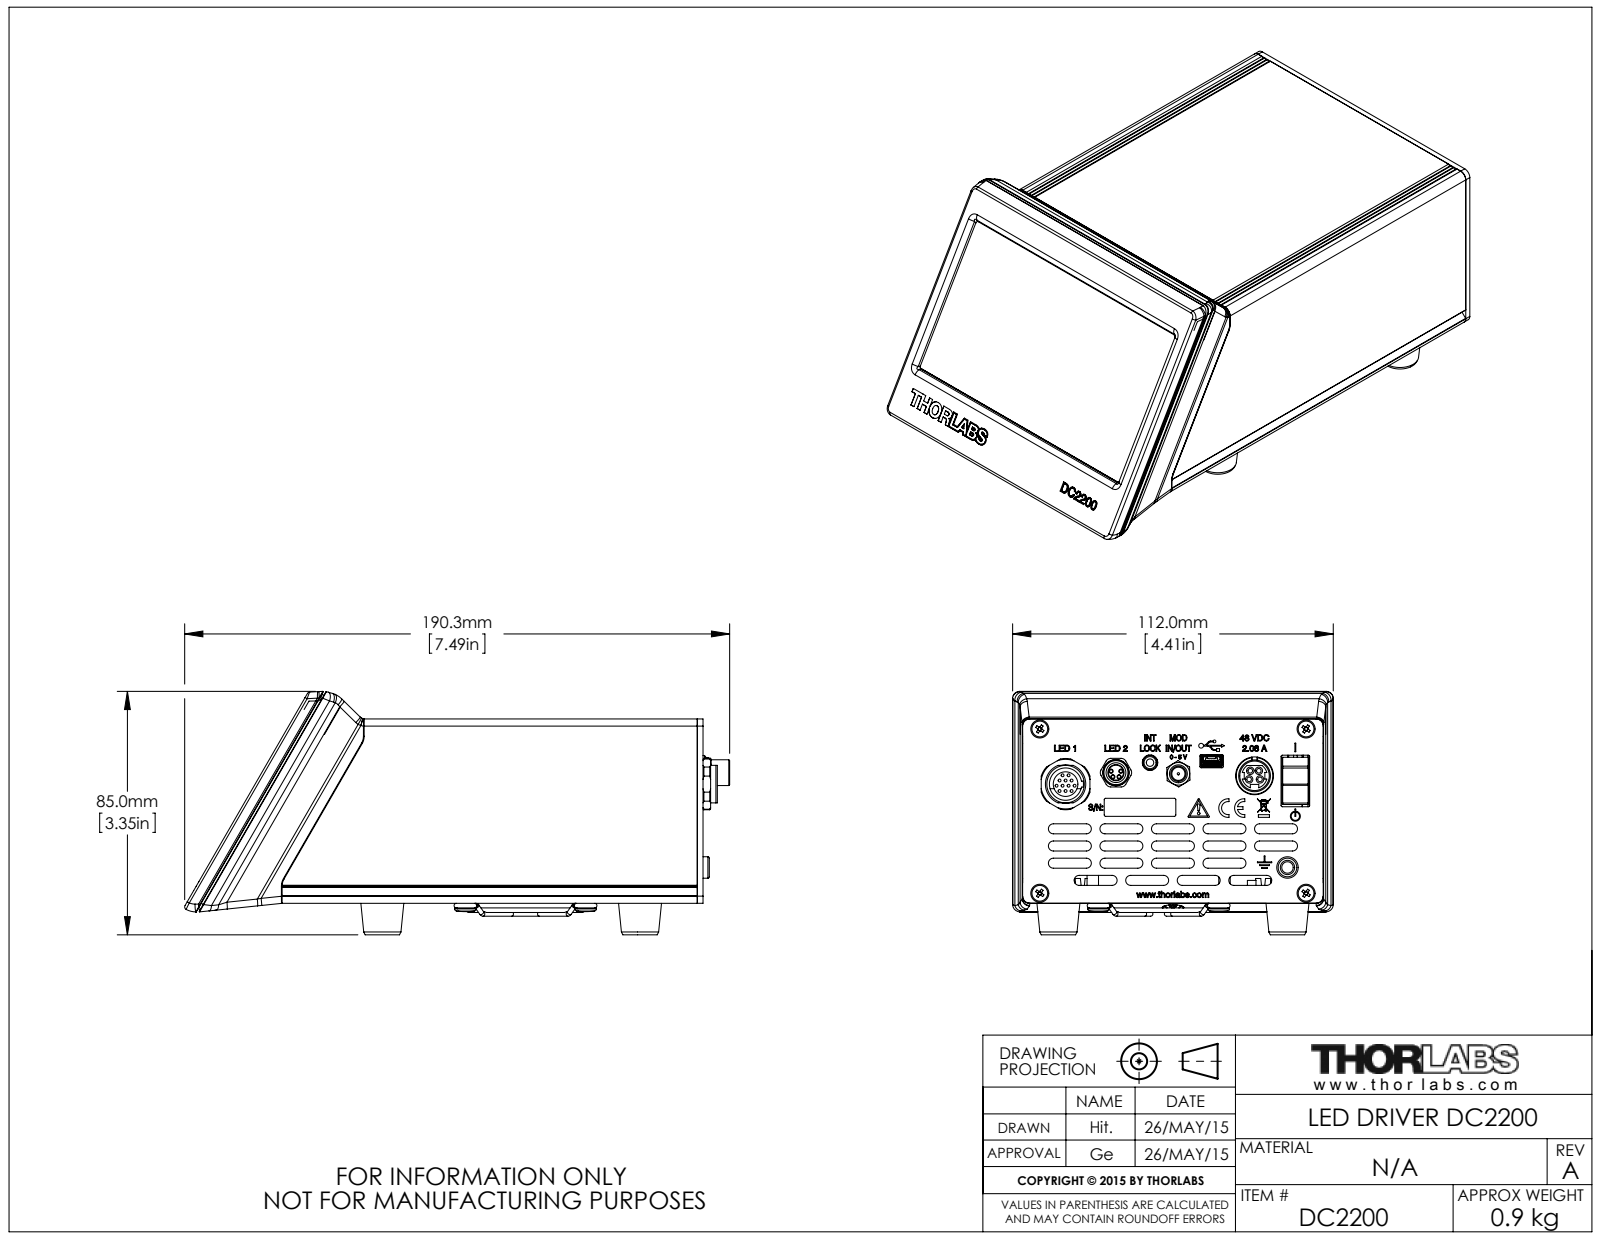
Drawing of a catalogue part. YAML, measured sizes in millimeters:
part_name: "Zusammenbau für Web"
step_written_by: "SolidWorks 2014 (AUTOMOTIVE_DESIGN)"
units: millimeters
bodies: {solids: 43, faces: 4882, planar: 2539, cylindrical: 1276, other: 1067}
overall_size: [190.33, 111.98, 84.99]
volume: 228259
surface_area: 228956
round_holes:
  - {diameter: 1, count: 13}
  - {diameter: 4.2, count: 8}
  - {diameter: 1.05, count: 4}
  - {diameter: 1.6, count: 4}
  - {diameter: 1.63, count: 4}
  - {diameter: 3.2, count: 4}
  - {diameter: 3.3, count: 4}
  - {diameter: 4.5, count: 4}
  - {diameter: 7.8, count: 4}
  - {diameter: 2.8, count: 3}
  - {diameter: 3, count: 3}
  - {diameter: 4.66, count: 3}
round_bosses_or_shafts:
  - {diameter: 1.6, count: 16}
  - {diameter: 0.9, count: 13}
  - {diameter: 1.5, count: 12}
  - {diameter: 3, count: 9}
  - {diameter: 1, count: 9}
  - {diameter: 7.5, count: 5}
  - {diameter: 5.5, count: 5}
  - {diameter: 4, count: 5}
partial_cylinders:
  - {radius: 0.2, count: 148}
  - {radius: 0.5, count: 77}
  - {radius: 0.3, count: 57}
  - {radius: 1, count: 40}
  - {radius: 0.15, count: 38}
  - {radius: 1.75, count: 36}
  - {radius: 2.5, count: 28}
  - {radius: 0.1, count: 22}
face_to_face_distances: [2, 62.36, 64.36, 60.36, 1.5, 5, 1.8, 3.5, 105, 1.2]
hole_center_spacings: [2.1, 3.64, 4.2, 2.12, 5.56, 3.65, 4.22, 5.58]
